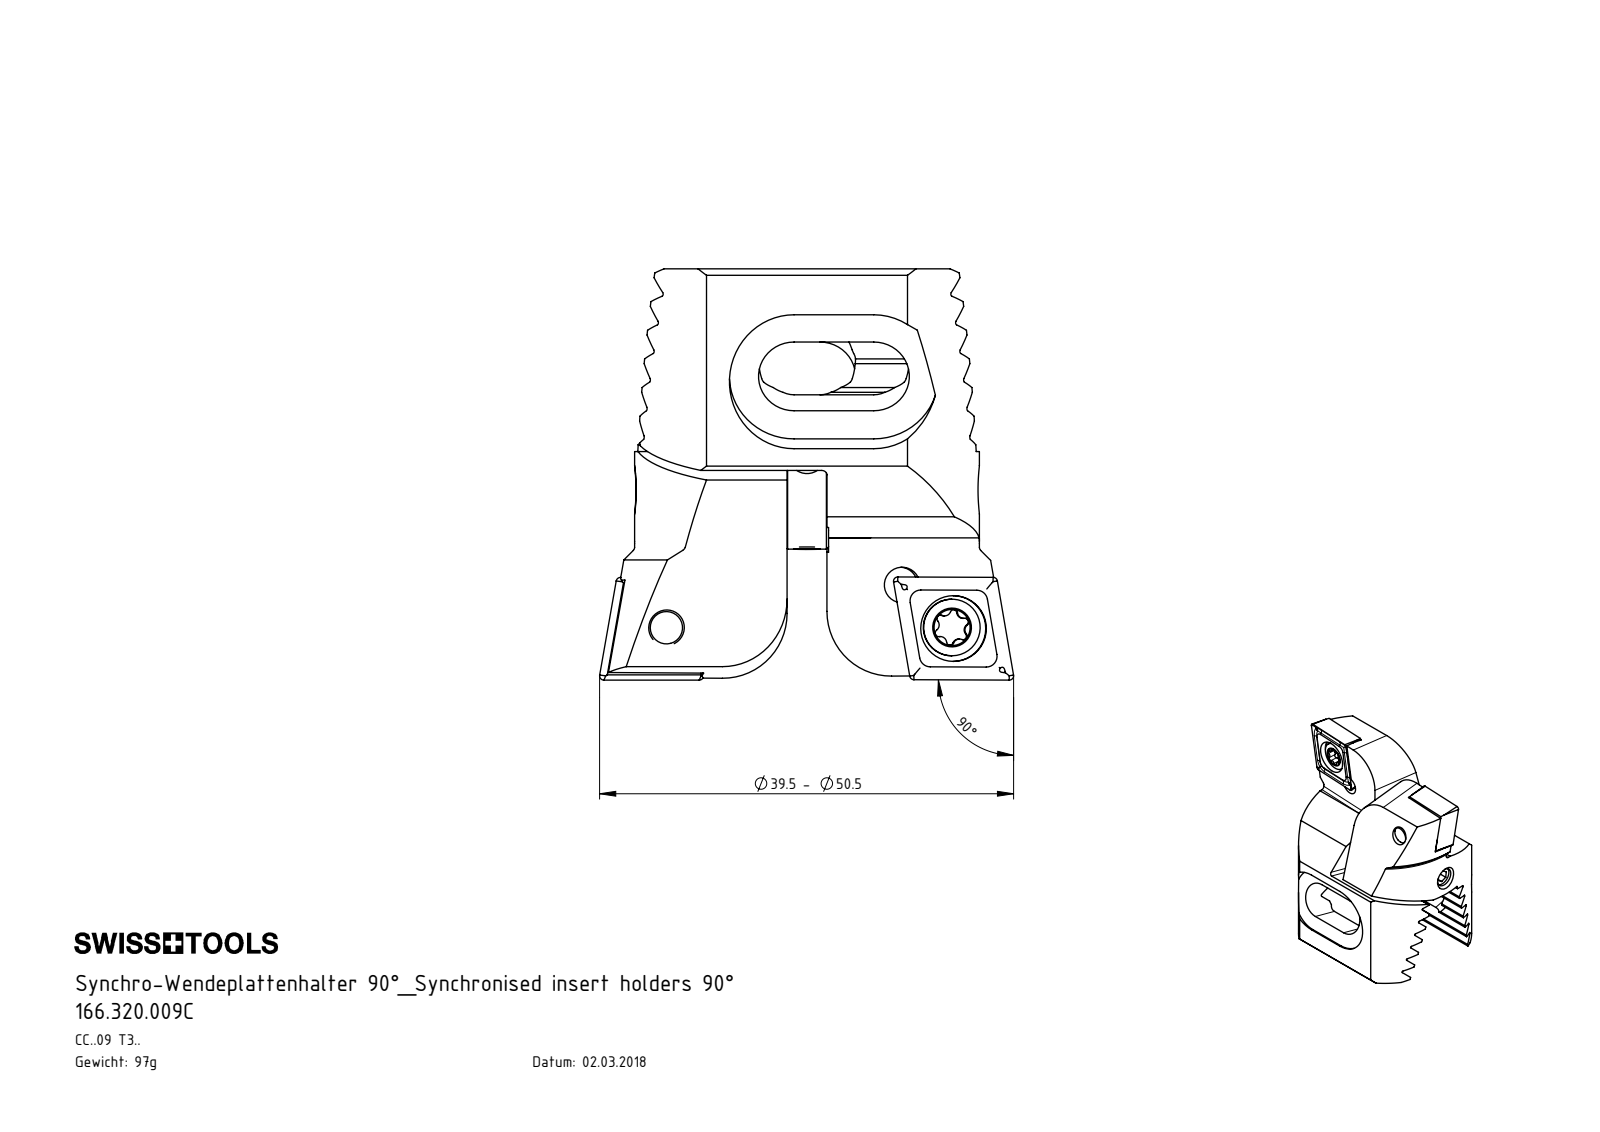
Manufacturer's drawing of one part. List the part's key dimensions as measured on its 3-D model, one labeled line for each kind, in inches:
Part name (STEP PRODUCT): CCMT09T304; Z32-WCB.003.021_A; Z25-ER3.002.004_B; WCB-ER2.001.009_A (+4 more)
STEP written by: SolidWorks 2017 (CONFIG_CONTROL_DESIGN)
Units: inches
Bodies: 11 solids, 503 faces (193 planar, 158 cylindrical, 152 other)
Overall size (bounding box): 1.513 × 1.502 × 1.031
Volume: 0.754 in³ · Surface area: 13.74 in²
Round holes (diameter × count): ⌀0.13 ×4, ⌀0.039 ×3, ⌀0.098 ×3, ⌀0.173 ×2, ⌀0.24 ×2, ⌀0.138 ×1
Round bosses / shafts (diameter × count): ⌀0.118 ×4, ⌀0.157 ×3, ⌀0.207 ×2, ⌀0.433 ×1
Partial cylindrical surfaces — rounded edges, fillets, slot ends (radius × count): R0.008 ×12, R0.013 ×12, R0.023 ×12, R0.039 ×8, R0.236 ×6, R0.02 ×4, R0.13 ×4, R0.63 ×2
Main face-to-face distances: 0.094, 0.375, 0.281, 0.187, 0.469, 0.152, 0.188, 0.032, 0.161, 0.379
Hole centre spacings: 0.394, 1.066, 0.079, 0.24, 0.24, 0.246, 0.246, 0.402
